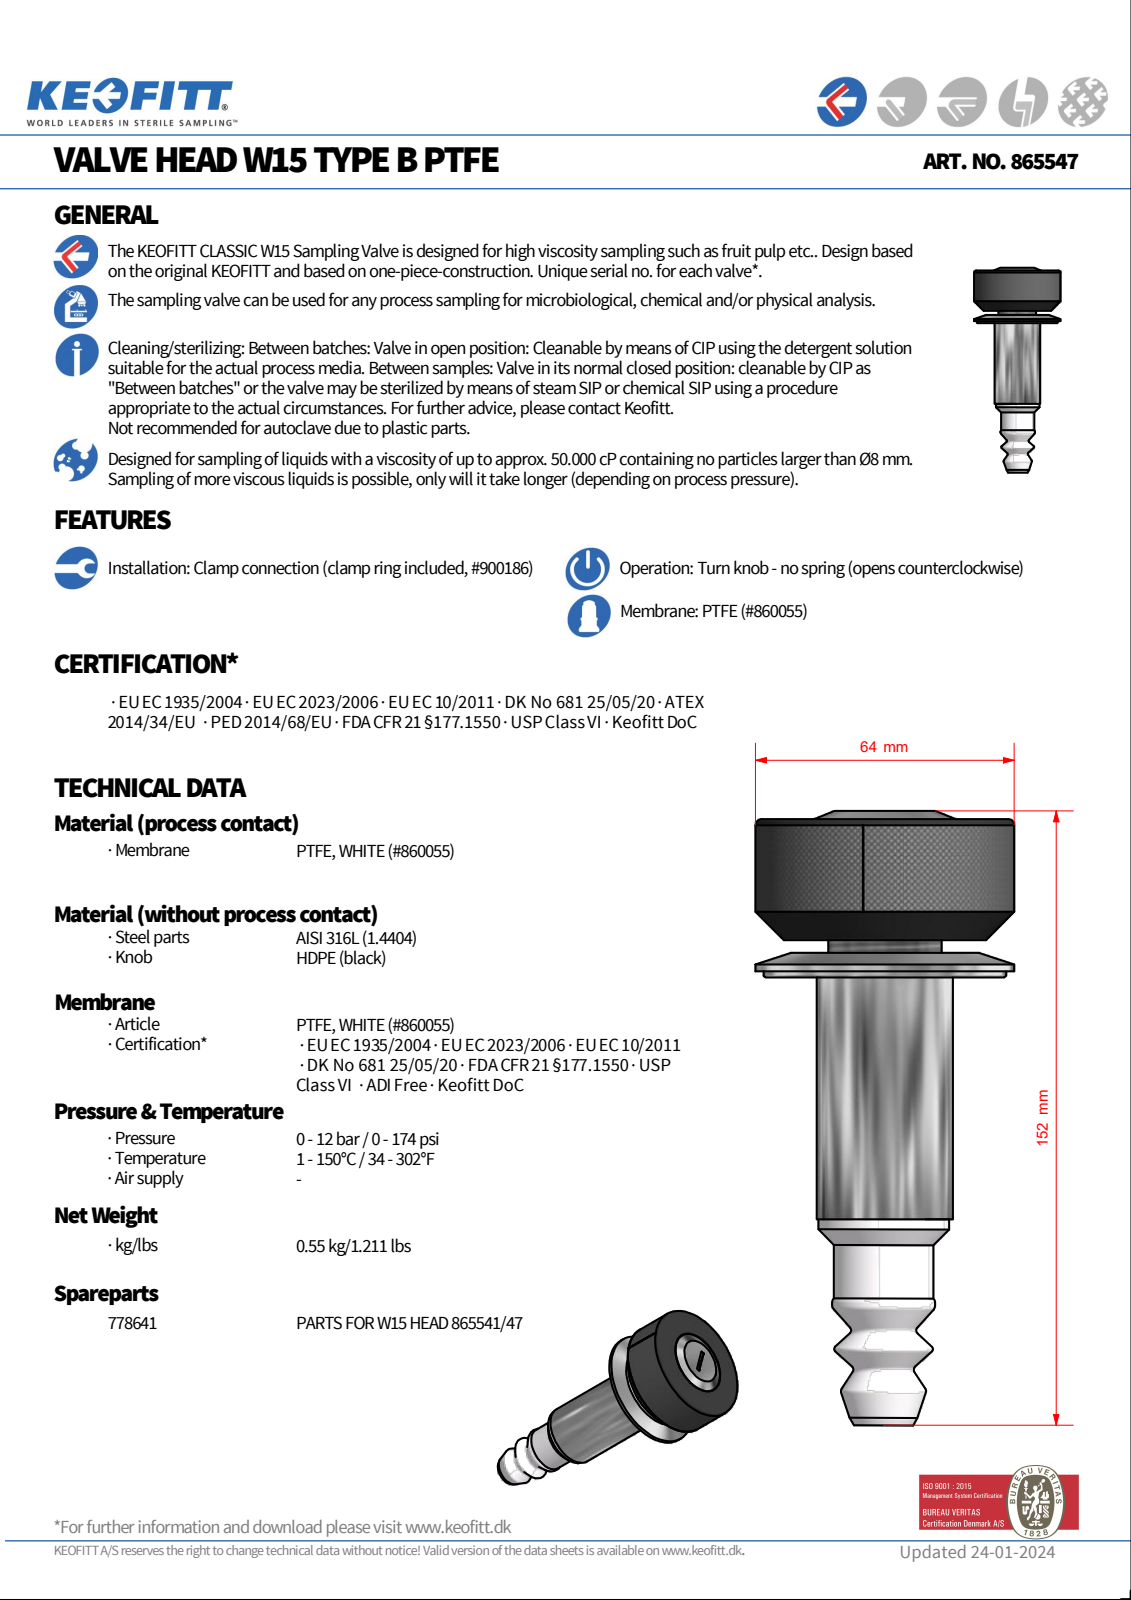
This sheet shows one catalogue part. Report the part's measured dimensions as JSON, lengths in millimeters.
{"part_name": "865547", "step_written_by": "Autodesk Inventor 2024 (AUTOMOTIVE_DESIGN)", "units": "millimeters", "bodies": {"solids": 1, "faces": 4358, "planar": 84, "cylindrical": 105, "other": 4169}, "overall_size": [154.9, 120.94, 86.61], "volume_mm3": 217272, "surface_area_mm2": 42146, "round_holes": [[64, 1]], "round_bosses_or_shafts": [[68.6, 1], [60, 1], [35, 1], [33.7, 1], [32.4, 1], [25.5, 1], [24.64, 1], [19.6, 1]], "partial_cylinders_radius": [[1, 40], [2, 21], [4, 4], [0.4, 2], [4.3, 2], [5.1, 2], [5.95, 2], [6.5, 1]], "face_to_face_distances": [36.1, 8.4, 1.8, 4.2, 7.8, 28.3, 16.2, 44.5, 2, 2.4]}
